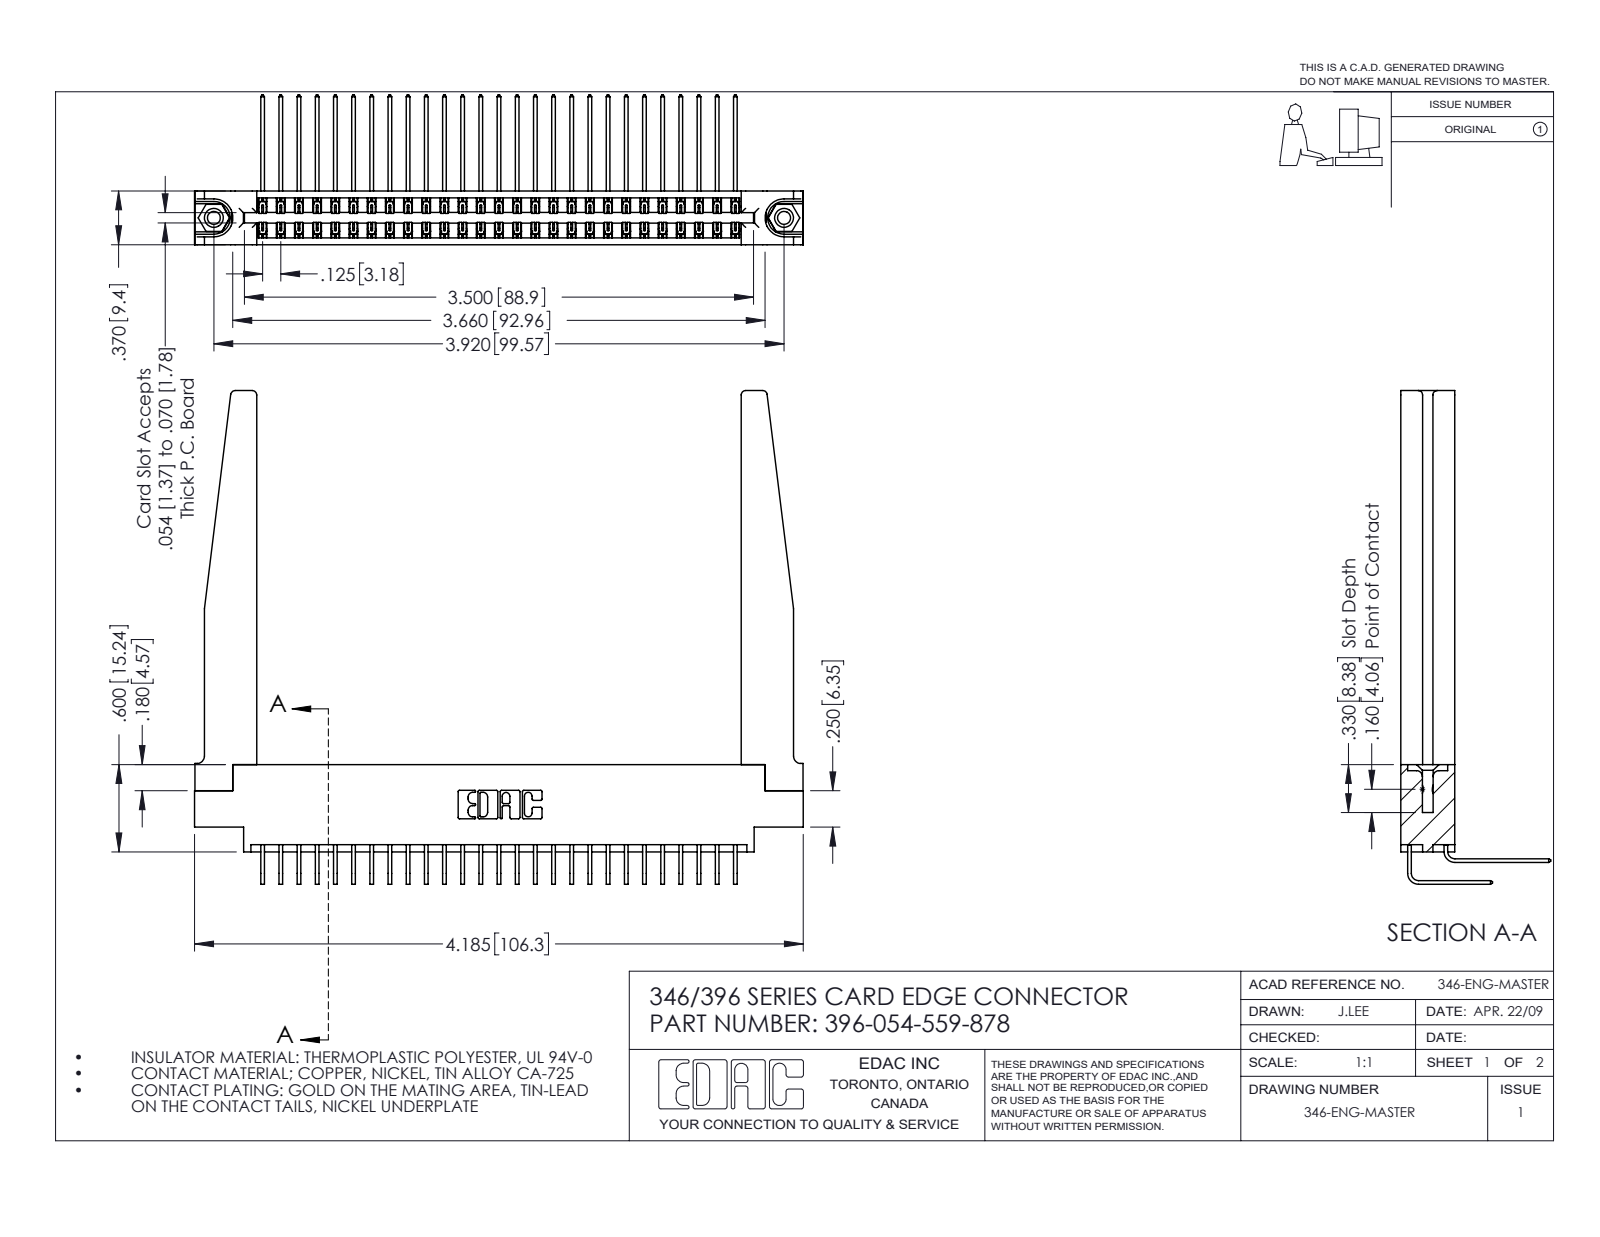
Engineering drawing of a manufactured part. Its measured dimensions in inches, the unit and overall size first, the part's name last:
Units: inches
Overall size (bounding box): 4.185 × 3.393 × 1.03
Round holes (diameter × count): ⌀0.089 ×2, ⌀0.125 ×2, ⌀0.156 ×2, ⌀0.064 ×1
Round bosses / shafts (diameter × count): ⌀0.155 ×2
Partial cylindrical surfaces — rounded edges, fillets, slot ends (radius × count): R0.006 ×81, R0.01 ×22, R0.03 ×8, R0.007 ×6, R0.031 ×6, R0.05 ×4, R0.026 ×3, R0.014 ×2
Main face-to-face distances: 0.37, 0.048, 0.322, 0.072, 0.025, 0.148, 0.15, 0.25, 0.298, 0.275
Hole centre spacings: 0.246, 3.712, 3.92
Volume: 1.057 in³ · Surface area: 34.53 in²
Bodies: 59 solids, 3276 faces (2220 planar, 1004 cylindrical, 52 other)
Part name (STEP PRODUCT): 396-054-559-878; 345-250-001_345-250-001-102; 346-220-078_345-220-078; 345-292-001_558 559 Tail - 1 (+2 more)
STEP written by: SolidWorks 2016 (CONFIG_CONTROL_DESIGN)
